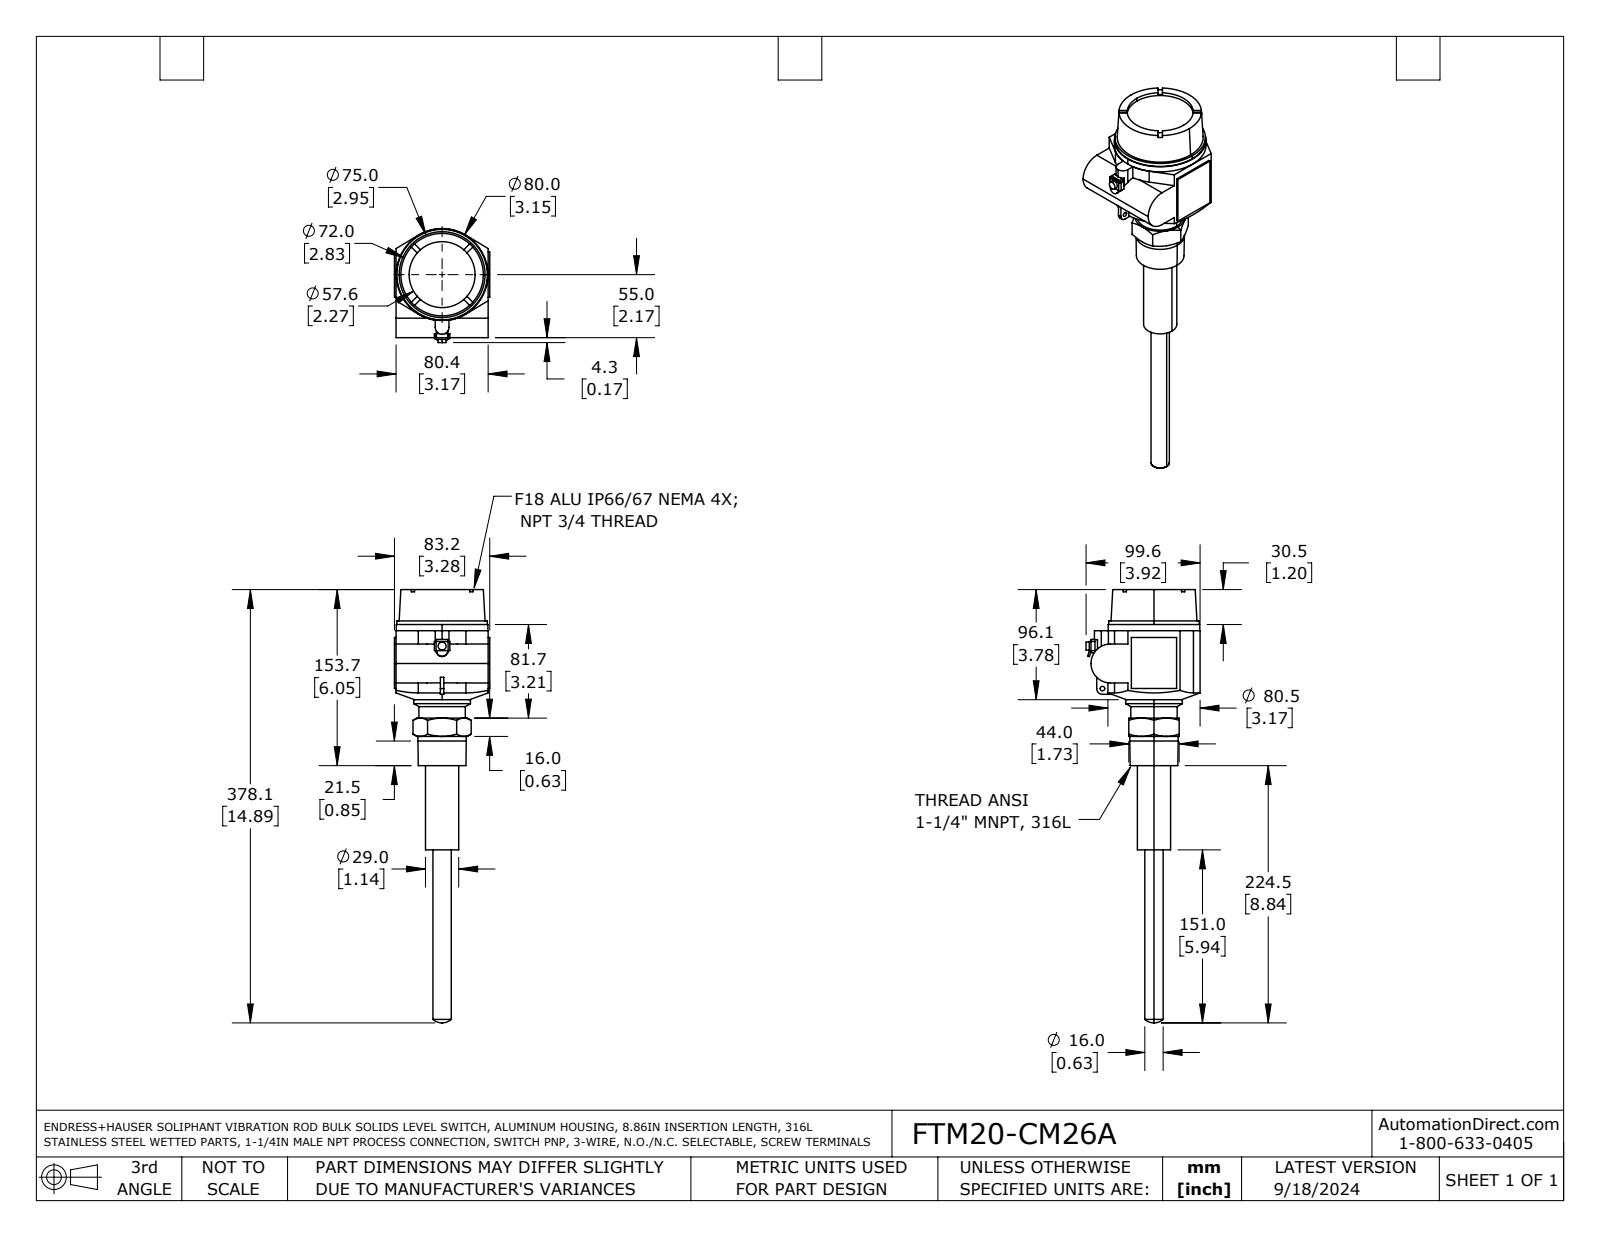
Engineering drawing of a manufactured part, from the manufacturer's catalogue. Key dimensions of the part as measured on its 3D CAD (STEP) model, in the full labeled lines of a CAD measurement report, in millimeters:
Part name (STEP PRODUCT): FTM20-CM26A
STEP written by: SolidWorks 2021 (AUTOMOTIVE_DESIGN)
Units: millimetres
Bodies: 1 solid, 151 faces (88 planar, 36 cylindrical, 27 other)
Overall size (bounding box): 378.2 × 99.5 × 83.2
Volume: 684 200 mm³ · Surface area: 62 420 mm²
Round holes (diameter × count): ⌀4 ×1, ⌀57.6 ×1
Round bosses / shafts (diameter × count): ⌀80 ×1, ⌀79 ×1, ⌀49.5 ×1, ⌀42.2 ×1, ⌀40.5 ×1, ⌀29 ×1, ⌀16 ×1, ⌀7 ×1
Partial cylindrical surfaces — rounded edges, fillets, slot ends (radius × count): R1.5 ×3, R5 ×2, R6 ×1, R17 ×1, R40.3 ×1
Main face-to-face distances: 1.4, 81.8, 83.2, 80.4, 3, 44, 80.5, 150.6, 153.6, 117.8
